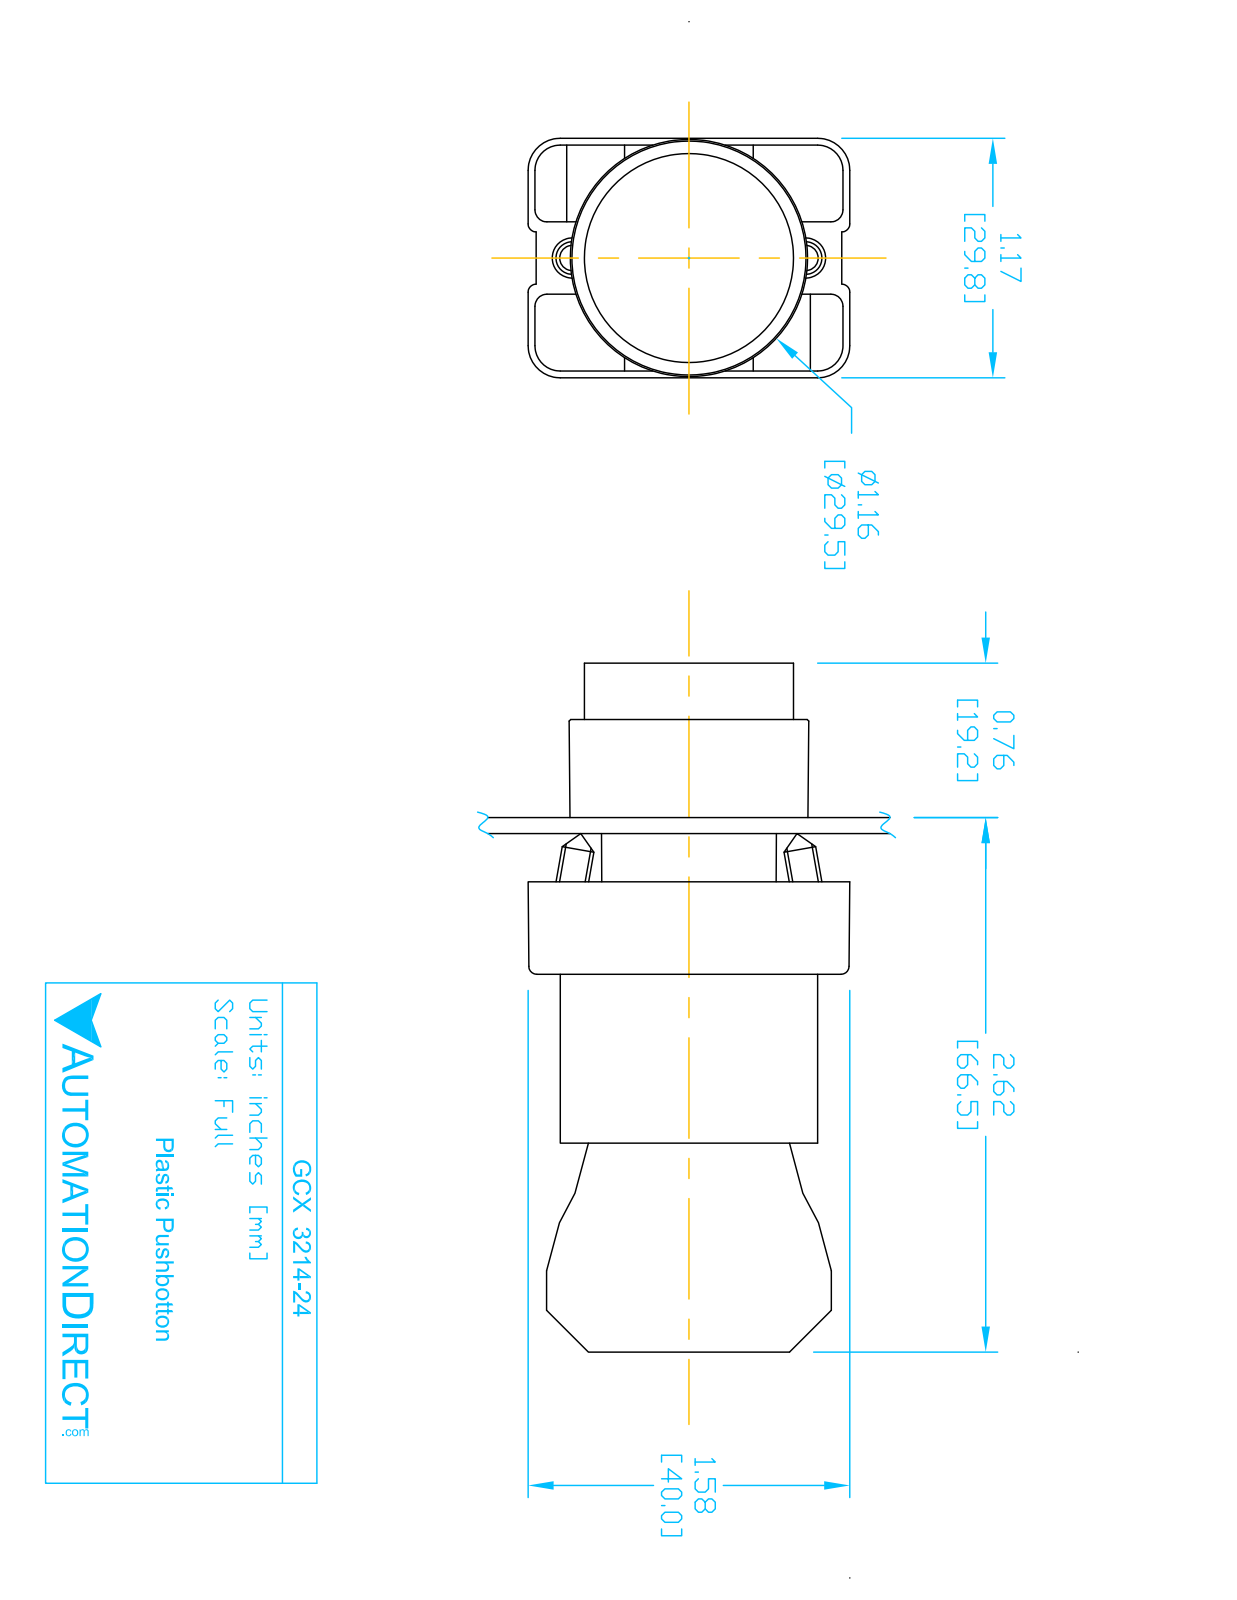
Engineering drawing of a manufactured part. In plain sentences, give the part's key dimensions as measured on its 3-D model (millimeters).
The part is named "ECX3029-2; ECX1050; GCX3214-24; GCX3214 OPERATOR (+1 more)". Its 3-D file was written by "SolidWorks 2016 (AUTOMOTIVE_DESIGN)". It is 7 solids with 425 faces: 250 planar, 144 cylindrical and 31 other. Overall it measures 84.3 by 40.2 by 29.9 millimeters. Its volume is 44 590 cubic millimeters and its surface area 23 430 square millimeters. Round holes: 2 of diameter 2, 2 of diameter 3.1, 2 of diameter 3.3, 1 of diameter 2.2, 1 of diameter 5, 1 of diameter 11.9, 1 of diameter 22.3, 1 of diameter 22.6, 1 of diameter 26. Round bosses or shafts: 4 of diameter 4, 1 of diameter 29.8, 1 of diameter 25.5, 1 of diameter 24, 1 of diameter 21.7, 1 of diameter 19.8, 1 of diameter 12.8. Partial cylindrical surfaces (rounded edges, fillets, slot ends): 24 of radius 1.5, 12 of radius 1, 12 of radius 3.1, 12 of radius 4, 8 of radius 1, 2 of radius 3.3, 1 of radius 0.5, 1 of radius 1.6. The main face-to-face distances are 21, 14.7, 29.7, 51.3, 30.3, 0.8, 0.8, 14.6, 29.6, 15.1. The hole center spacings are 6, 13.8, 12, 12.4.
